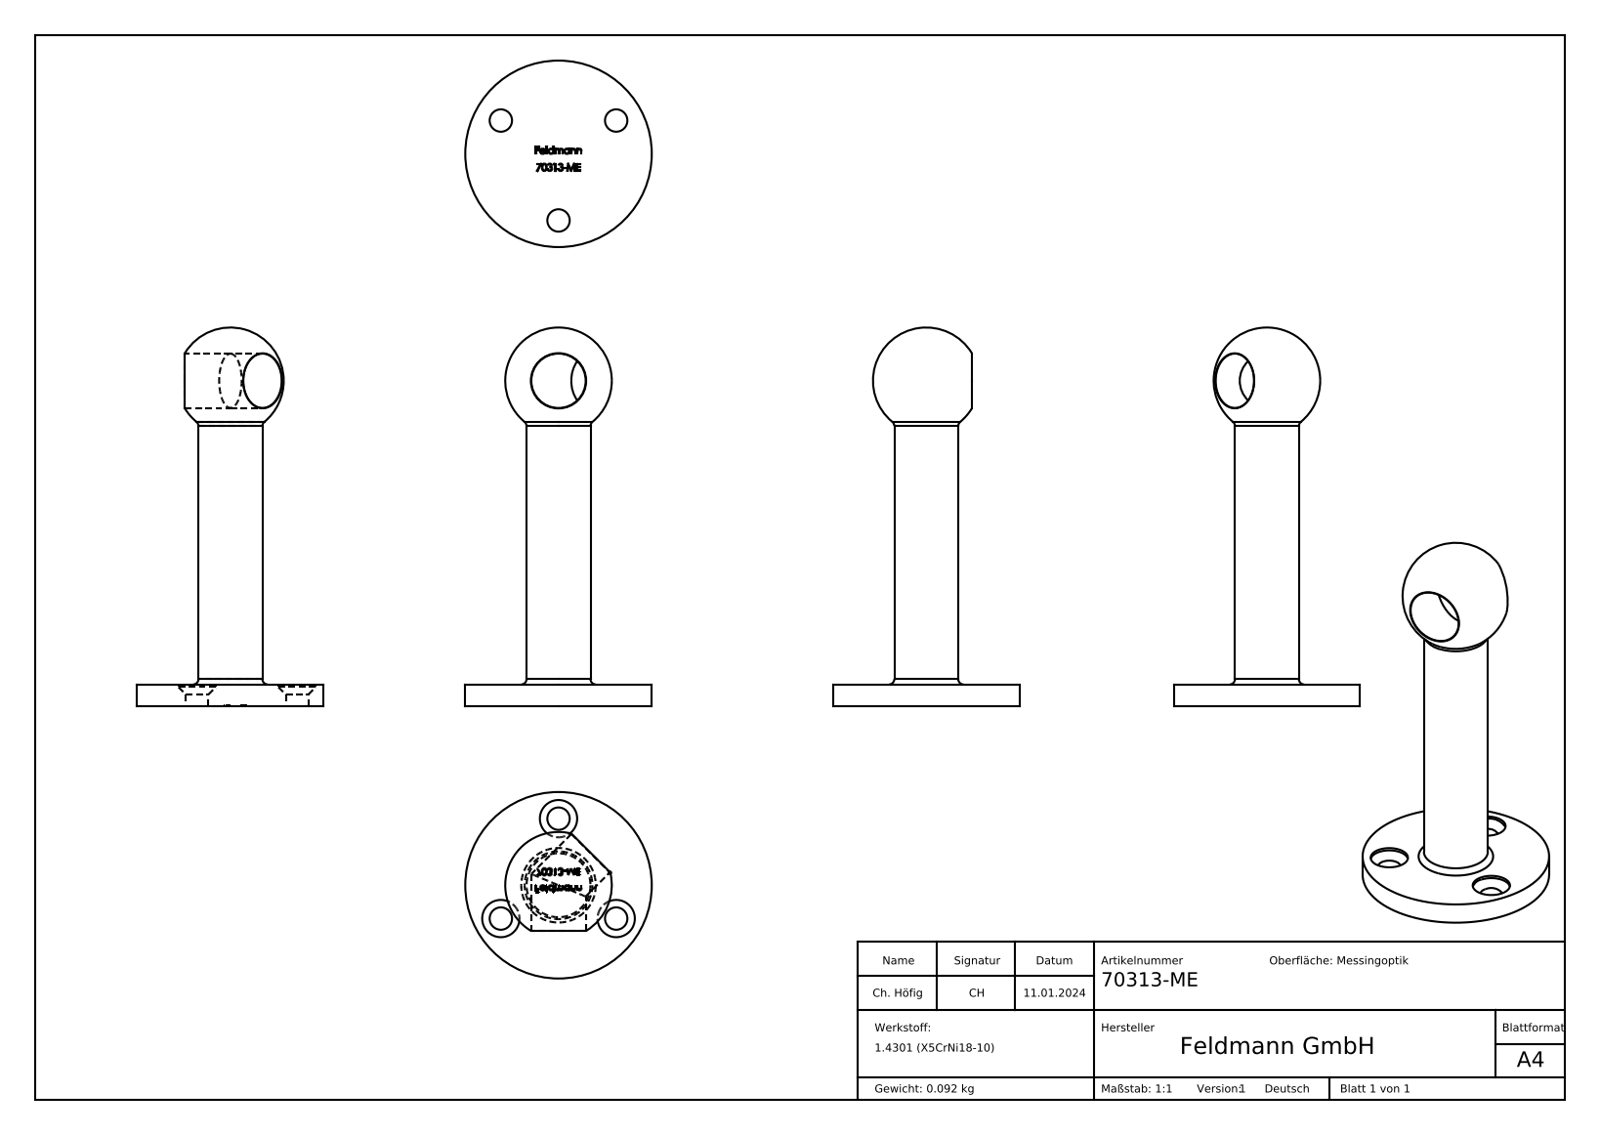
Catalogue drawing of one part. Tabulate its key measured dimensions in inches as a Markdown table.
| quantity | value |
| --- | --- |
| part name | 70313-ME |
| STEP written by | SolidWorks 2018 (CONFIG_CONTROL_DESIGN) |
| units | inches |
| bodies | 1 solid, 231 faces (118 planar, 10 cylindrical, 103 other) |
| overall size | 2.795 × 1.378 × 1.378 |
| volume | 0.714 in³ |
| surface area | 8.764 in² |
| round holes (diameter × count) | 0.165 × 3, 0.276 × 3, 0.402 × 2 |
| round bosses / shafts (diameter × count) | 1.378 × 1, 0.472 × 1 |
| main face-to-face distances | 0.157, 0.154, 0.117, 0.015, 0.055, 0.133, 0.126, 0.144, 0.161, 0.044 |
| hole center spacings | 0.852, 0.853 |
